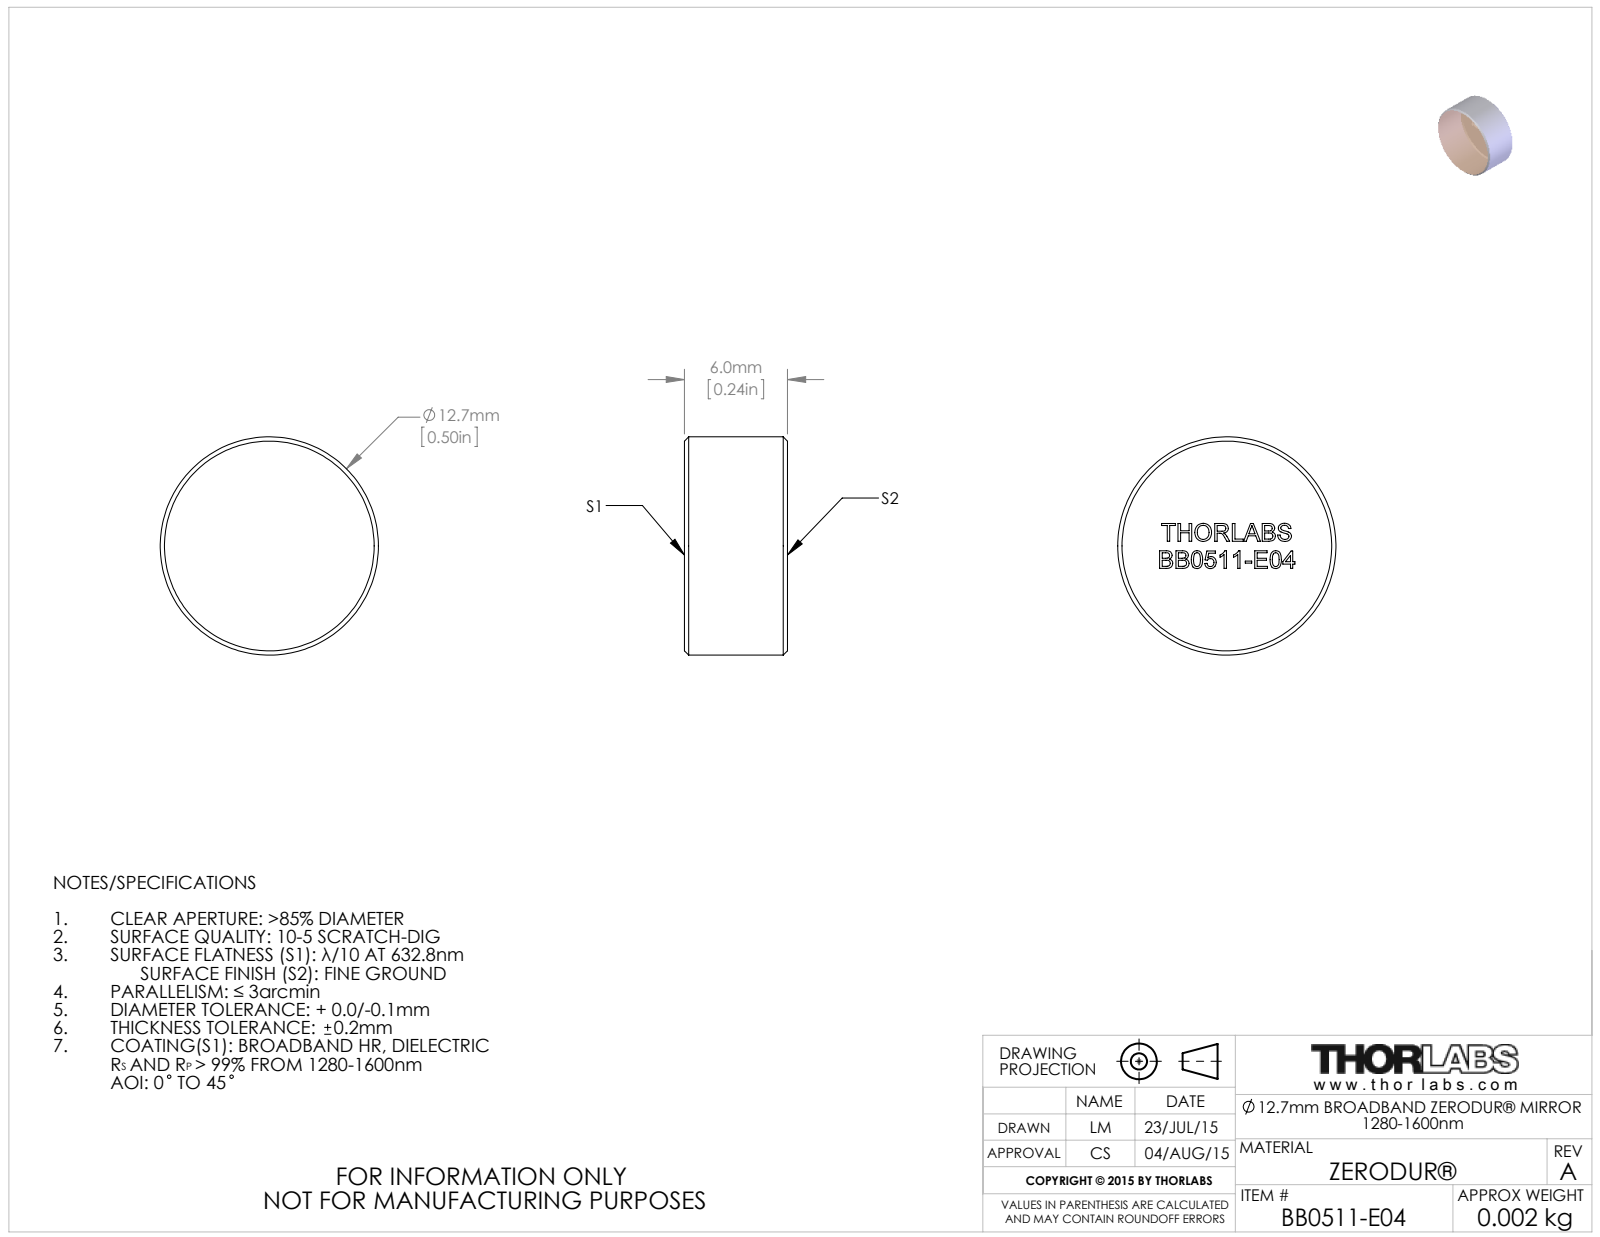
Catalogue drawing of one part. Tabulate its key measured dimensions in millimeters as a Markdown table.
| quantity | value |
| --- | --- |
| part name | TTN045135-E0W |
| STEP written by | SolidWorks 2014 (CONFIG_CONTROL_DESIGN) |
| units | millimeters |
| bodies | 1 solid, 257 faces (156 planar, 2 cylindrical, 99 other) |
| overall size | 12.7 × 12.7 × 6 |
| volume | 758 mm³ |
| surface area | 481 mm² |
| round bosses / shafts (diameter × count) | 12.7 × 1 |
| main face-to-face distances | 6, 1.58, 0.44, 0.79, 0.91, 1.03, 1.46, 1.28, 2.02, 0.67 |
